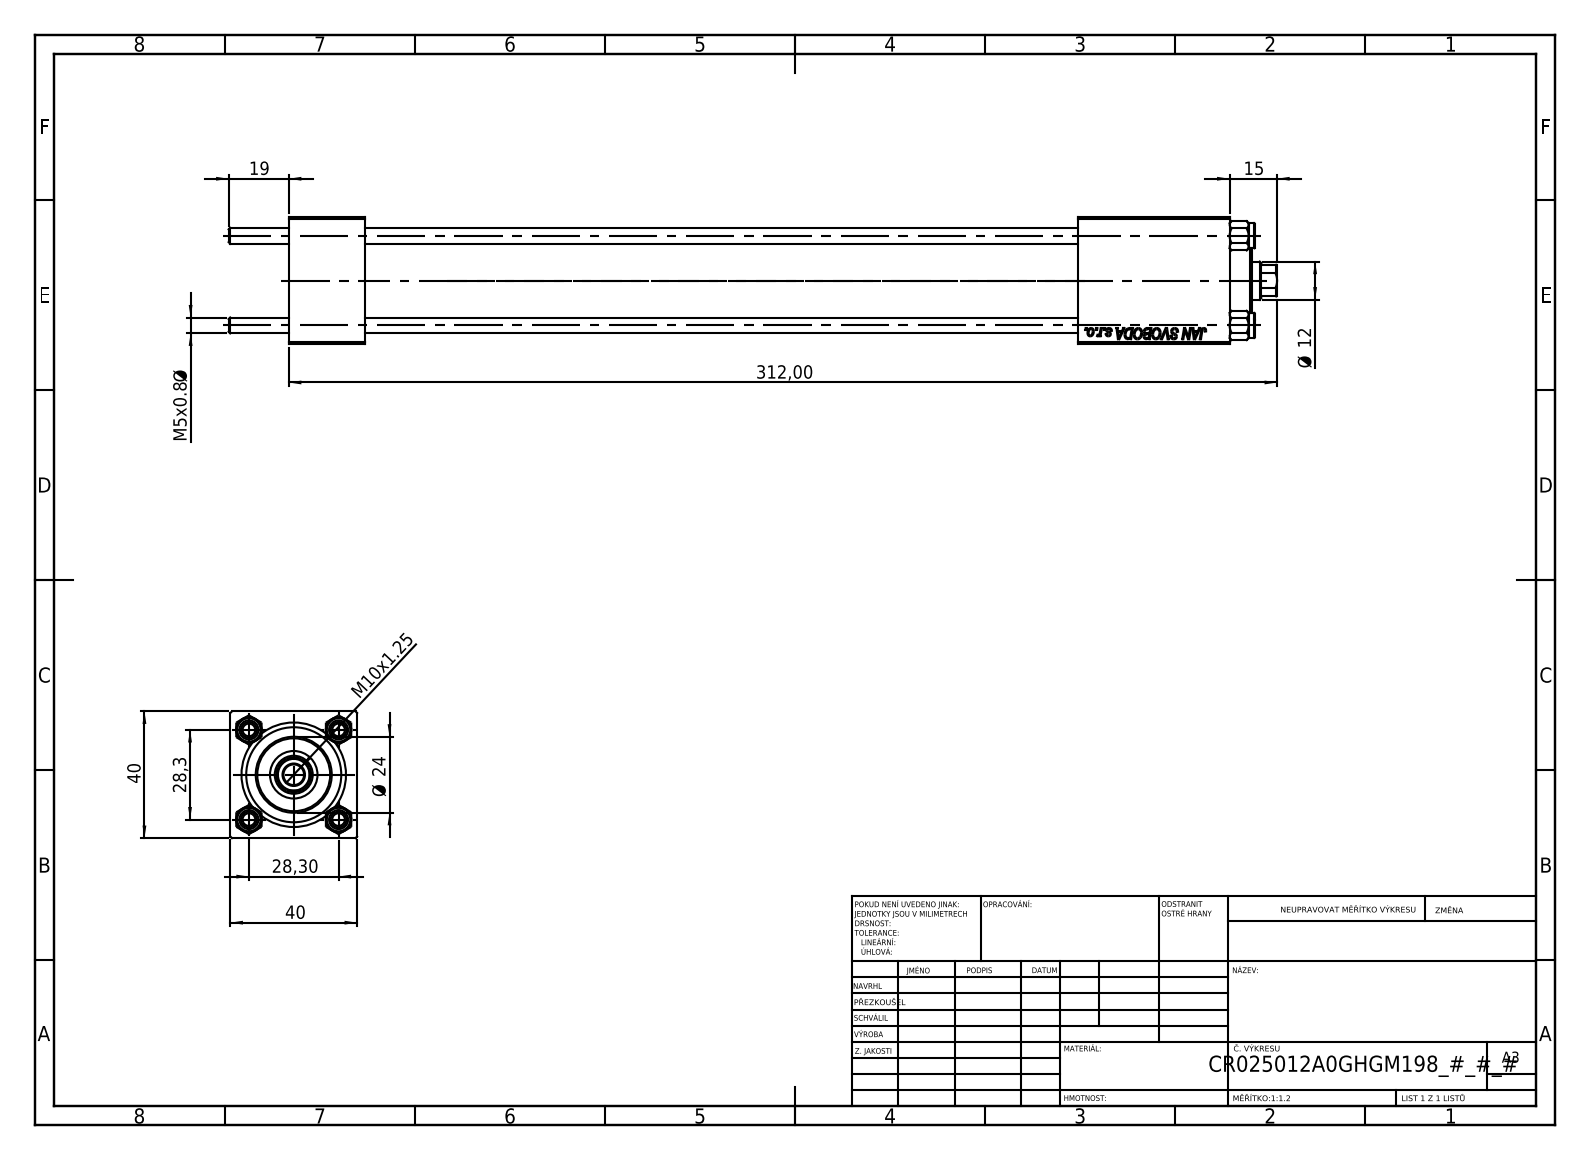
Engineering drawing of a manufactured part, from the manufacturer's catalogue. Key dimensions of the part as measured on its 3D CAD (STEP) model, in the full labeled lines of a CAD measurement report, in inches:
Part name (STEP PRODUCT): V215_VC_A; NUT_M5; CR025_012_A_0_G_A_G_M_020_+#_##_TYCINKA; V215CR_BODY_A (+1 more)
STEP written by: SolidWorks 2019 (CONFIG_CONTROL_DESIGN)
Units: inches
Bodies: 11 solids, 1131 faces (517 planar, 78 cylindrical, 536 other)
Overall size (bounding box): 13.031 × 1.575 × 1.575
Volume: 13.79 in³ · Surface area: 167.5 in²
Round holes (diameter × count): ⌀0.197 ×4, ⌀0.787 ×3, ⌀0.276 ×2, ⌀0.518 ×2, ⌀0.256 ×1, ⌀0.472 ×1, ⌀0.591 ×1, ⌀0.984 ×1, ⌀1.181 ×1
Round bosses / shafts (diameter × count): ⌀0.315 ×4, ⌀1.22 ×1, ⌀0.945 ×1
Partial cylindrical surfaces — rounded edges, fillets, slot ends (radius × count): R0.217 ×1
Main face-to-face distances: 1.575, 0.945, 11.693, 10.748, 10.563, 9.618, 1.13, 9.803, 8.858, 0.76
Hole centre spacings: 0.788, 1.114, 1.576, 9.843
